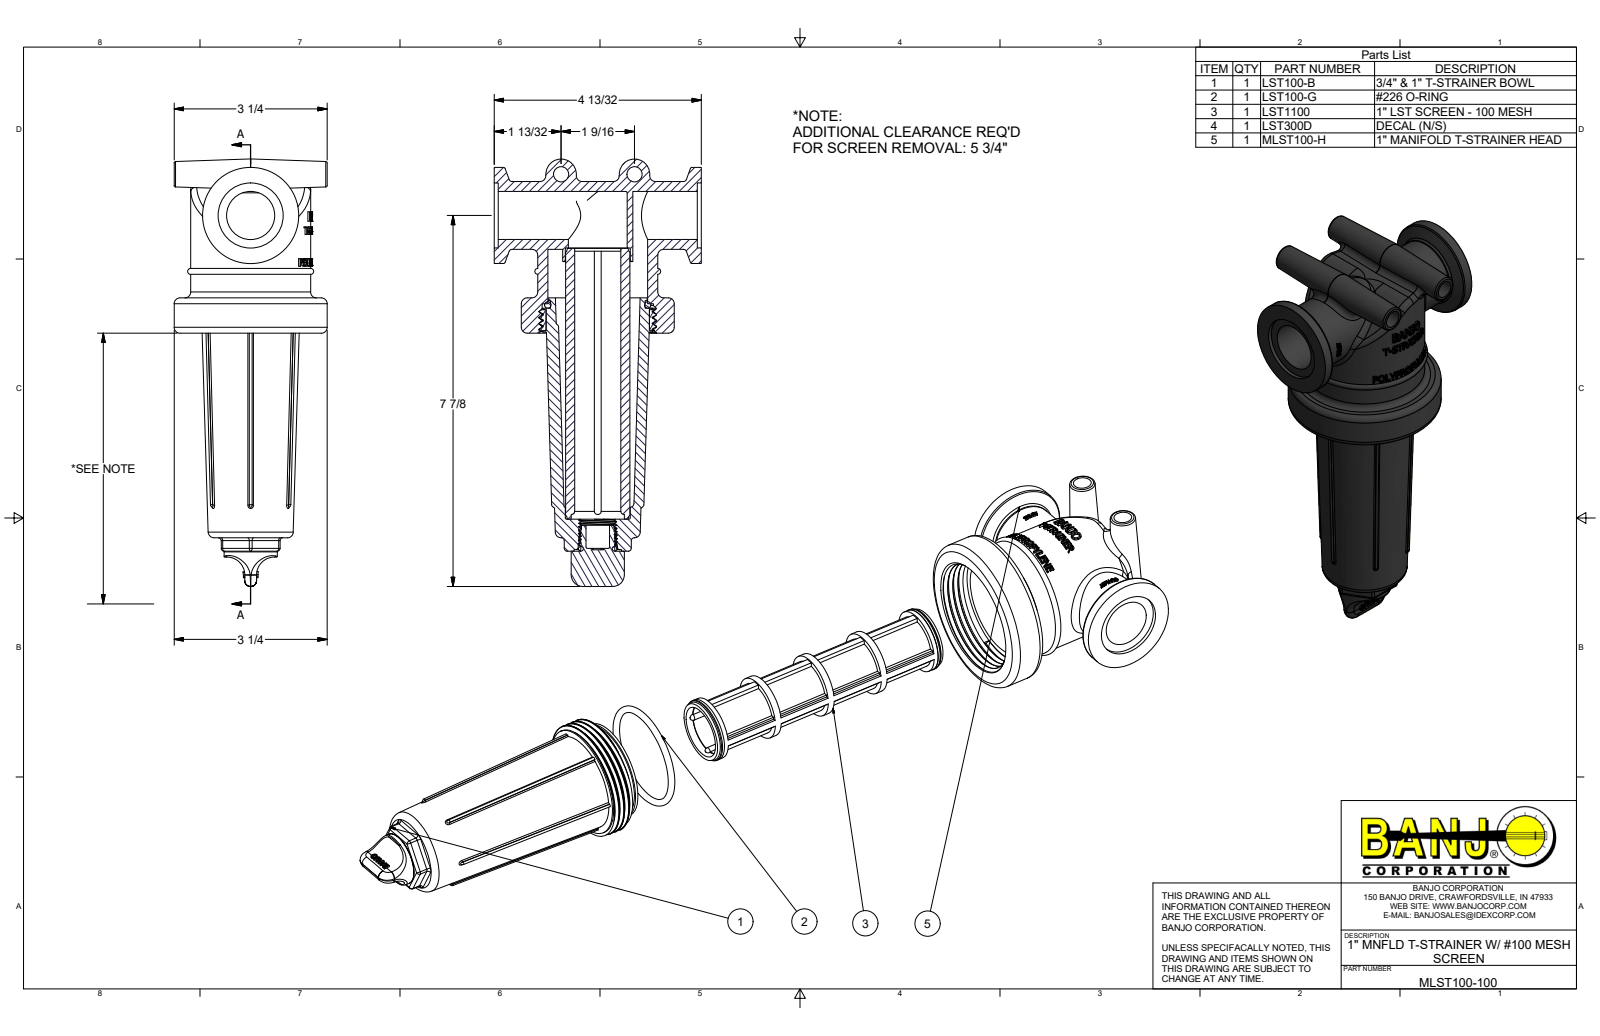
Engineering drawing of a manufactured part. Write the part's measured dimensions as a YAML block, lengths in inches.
part_name: "MLST100-100; MLST100-H; LST100-B; LST100-XB (+4 more)"
step_written_by: "Autodesk Inventor 2013 (AUTOMOTIVE_DESIGN)"
units: inches
bodies: {solids: 7, faces: 1343, planar: 695, cylindrical: 158, other: 490}
overall_size: [9.08, 4.4, 3.25]
volume: 18.92
surface_area: 252.3
round_holes:
  - {diameter: 1.38, count: 2}
  - {diameter: 0.5, count: 1}
  - {diameter: 0.98, count: 1}
  - {diameter: 1.005, count: 1}
  - {diameter: 1.02, count: 1}
  - {diameter: 1.1, count: 1}
  - {diameter: 1.25, count: 1}
  - {diameter: 2.12, count: 1}
  - {diameter: 2.195, count: 1}
  - {diameter: 2.365, count: 1}
round_bosses_or_shafts:
  - {diameter: 3.25, count: 1}
  - {diameter: 2.55, count: 1}
  - {diameter: 2.5, count: 1}
  - {diameter: 2.34, count: 1}
  - {diameter: 2.1, count: 1}
  - {diameter: 2.04, count: 1}
  - {diameter: 2.01, count: 1}
  - {diameter: 1.49, count: 1}
partial_cylinders:
  - {radius: 0.06, count: 19}
  - {radius: 0.03, count: 9}
  - {radius: 0.075, count: 4}
  - {radius: 0.38, count: 2}
  - {radius: 0.5, count: 1}
  - {radius: 0.75, count: 1}
  - {radius: 1.315, count: 1}
face_to_face_distances: [0.05, 1.35, 0.25, 0.03, 0.48, 0.75, 1.2, 0.15, 1.5, 2.125]
